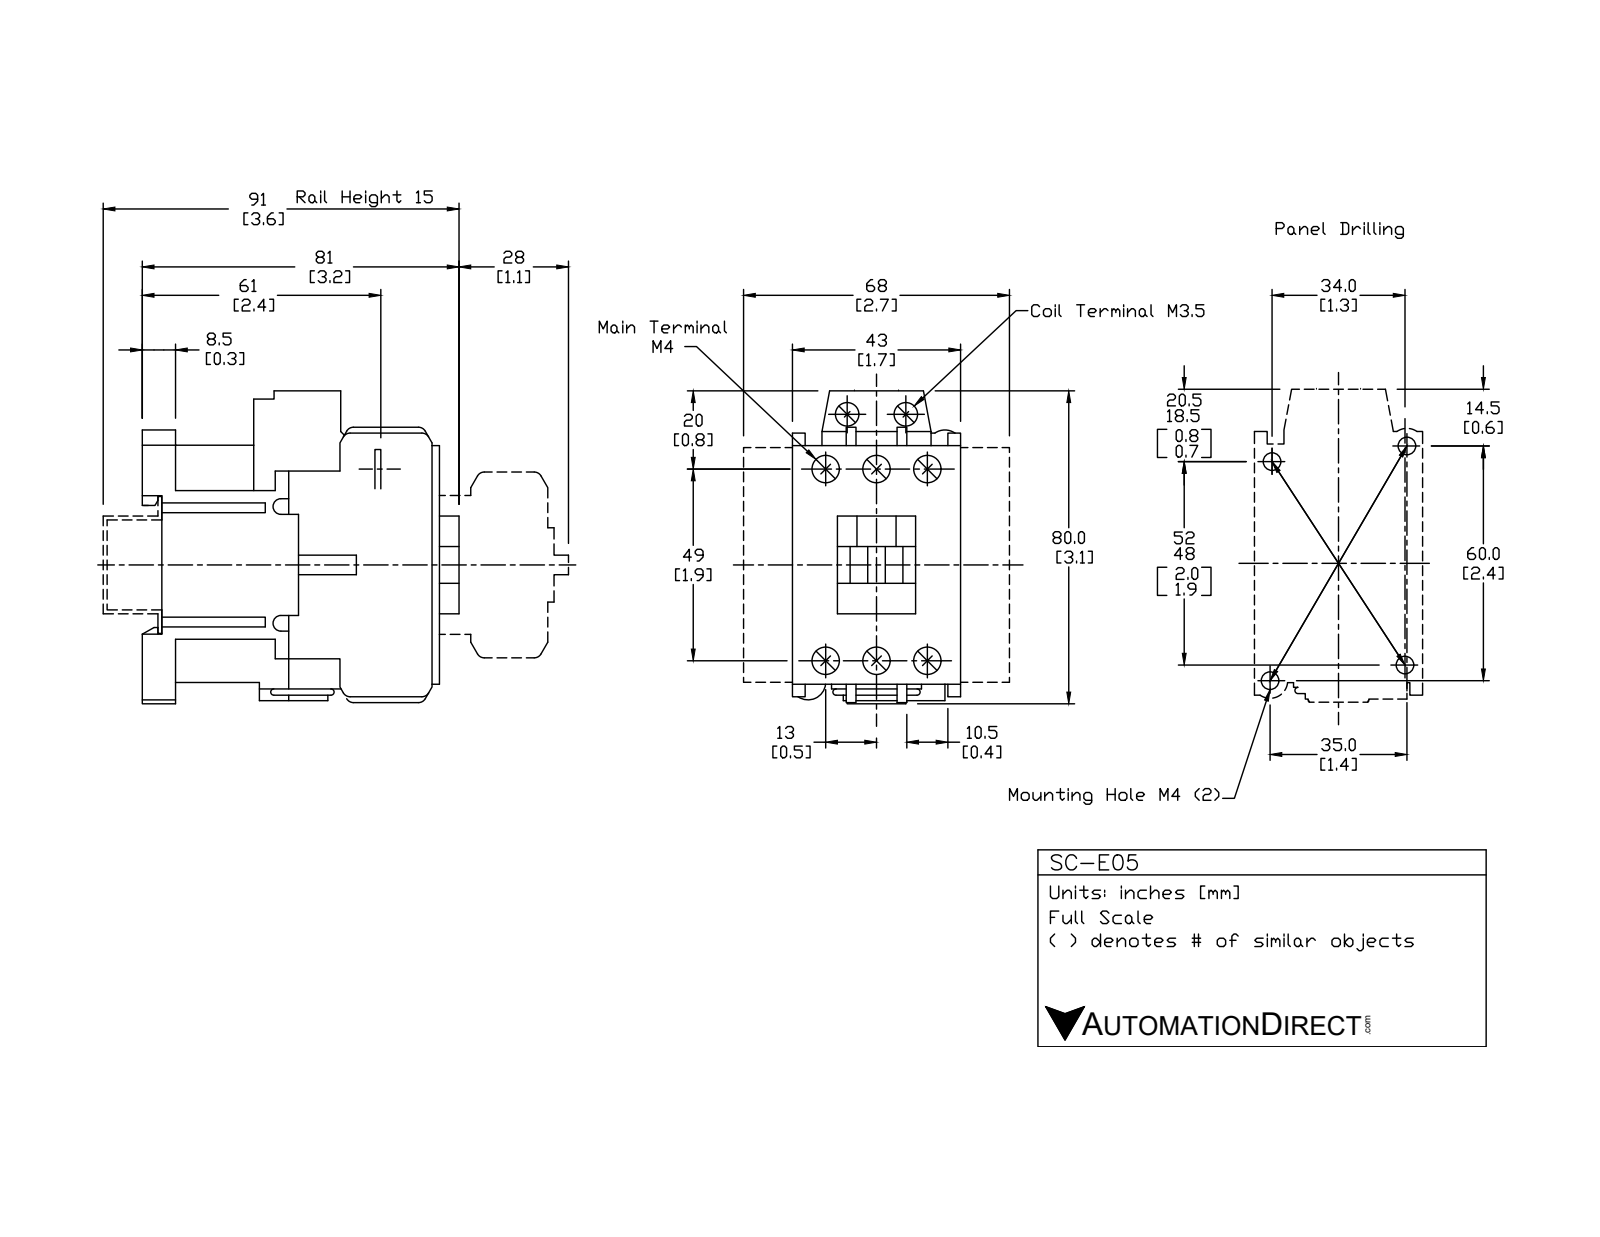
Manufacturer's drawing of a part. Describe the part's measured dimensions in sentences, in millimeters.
The part is named "SC-E05-110VAC". Its 3-D file was written by "SolidWorks 2015 (AUTOMOTIVE_DESIGN)". It is 1 solid with 1388 faces: 1148 planar, 192 cylindrical and 48 other. Overall it measures 81 by 81 by 43 millimeters. Its volume is 163 600 cubic millimeters and its surface area 42 360 square millimeters. Round holes: 6 of diameter 4.1, 6 of diameter 7, 2 of diameter 3.6, 2 of diameter 4.5, 2 of diameter 6.7, 1 of diameter 1.6. Round bosses or shafts: 6 of diameter 7.6, 6 of diameter 4, 2 of diameter 7.1, 2 of diameter 6.6, 2 of diameter 3.5. Partial cylindrical surfaces (rounded edges, fillets, slot ends): 32 of radius 1.5, 14 of radius 2, 10 of radius 0.5, 4 of radius 0.6, 4 of radius 2.3, 4 of radius 3.6, 2 of radius 4.1, 2 of radius 4.5. The main face-to-face distances are 43, 13, 10.5, 2.5, 23.5, 33, 16.3, 26.7, 15.5, 13.7. The hole center spacings are 13, 50.7, 49, 7.1, 7.6, 15, 15.9, 18.
